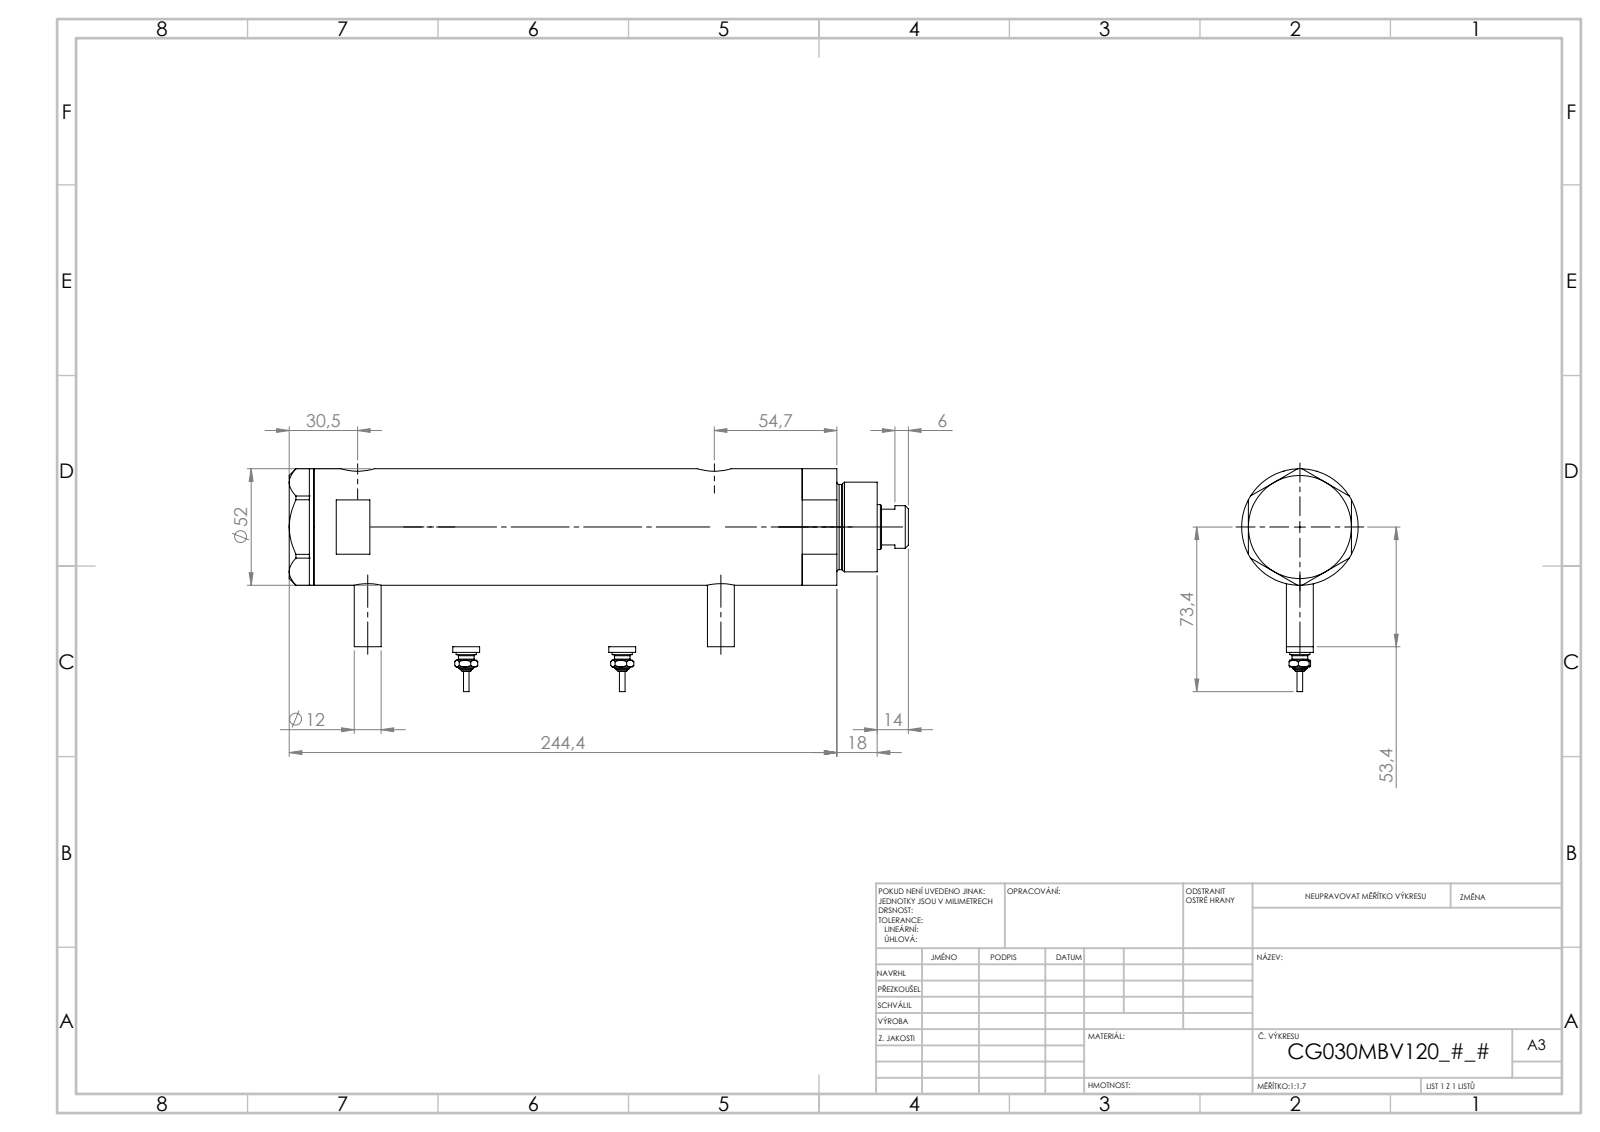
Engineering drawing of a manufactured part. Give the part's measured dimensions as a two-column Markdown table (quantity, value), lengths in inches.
| quantity | value |
| --- | --- |
| part name | V270CG_BACK; V270CG_FRONT; V270CG_VC; V270CG_MIDDLE (+1 more) |
| STEP written by | SolidWorks 2019 (CONFIG_CONTROL_DESIGN) |
| units | inches |
| bodies | 6 solids, 246 faces (95 planar, 77 cylindrical, 74 other) |
| overall size | 10.591 × 3.319 × 2.047 |
| volume | 29.18 in³ |
| surface area | 163.5 in² |
| round holes (diameter × count) | 0.197 × 2, 0.383 × 2, 0.492 × 2, 0.591 × 2, 0.256 × 1, 0.787 × 1, 0.846 × 1, 1.181 × 1, 1.299 × 1, 1.732 × 1 |
| round bosses / shafts (diameter × count) | 0.472 × 3, 0.354 × 2, 0.276 × 2, 0.171 × 2, 0.094 × 2, 2.047 × 1, 1.575 × 1, 1.496 × 1 |
| main face-to-face distances | 0.937, 0.433, 1.37, 1.811, 7.265, 6.832, 5.895, 8.698, 8.265, 7.328 |
| hole center spacings | 0.114, 0.177, 5.778, 5.892, 5.955, 6.069, 0.114, 0.115 |
